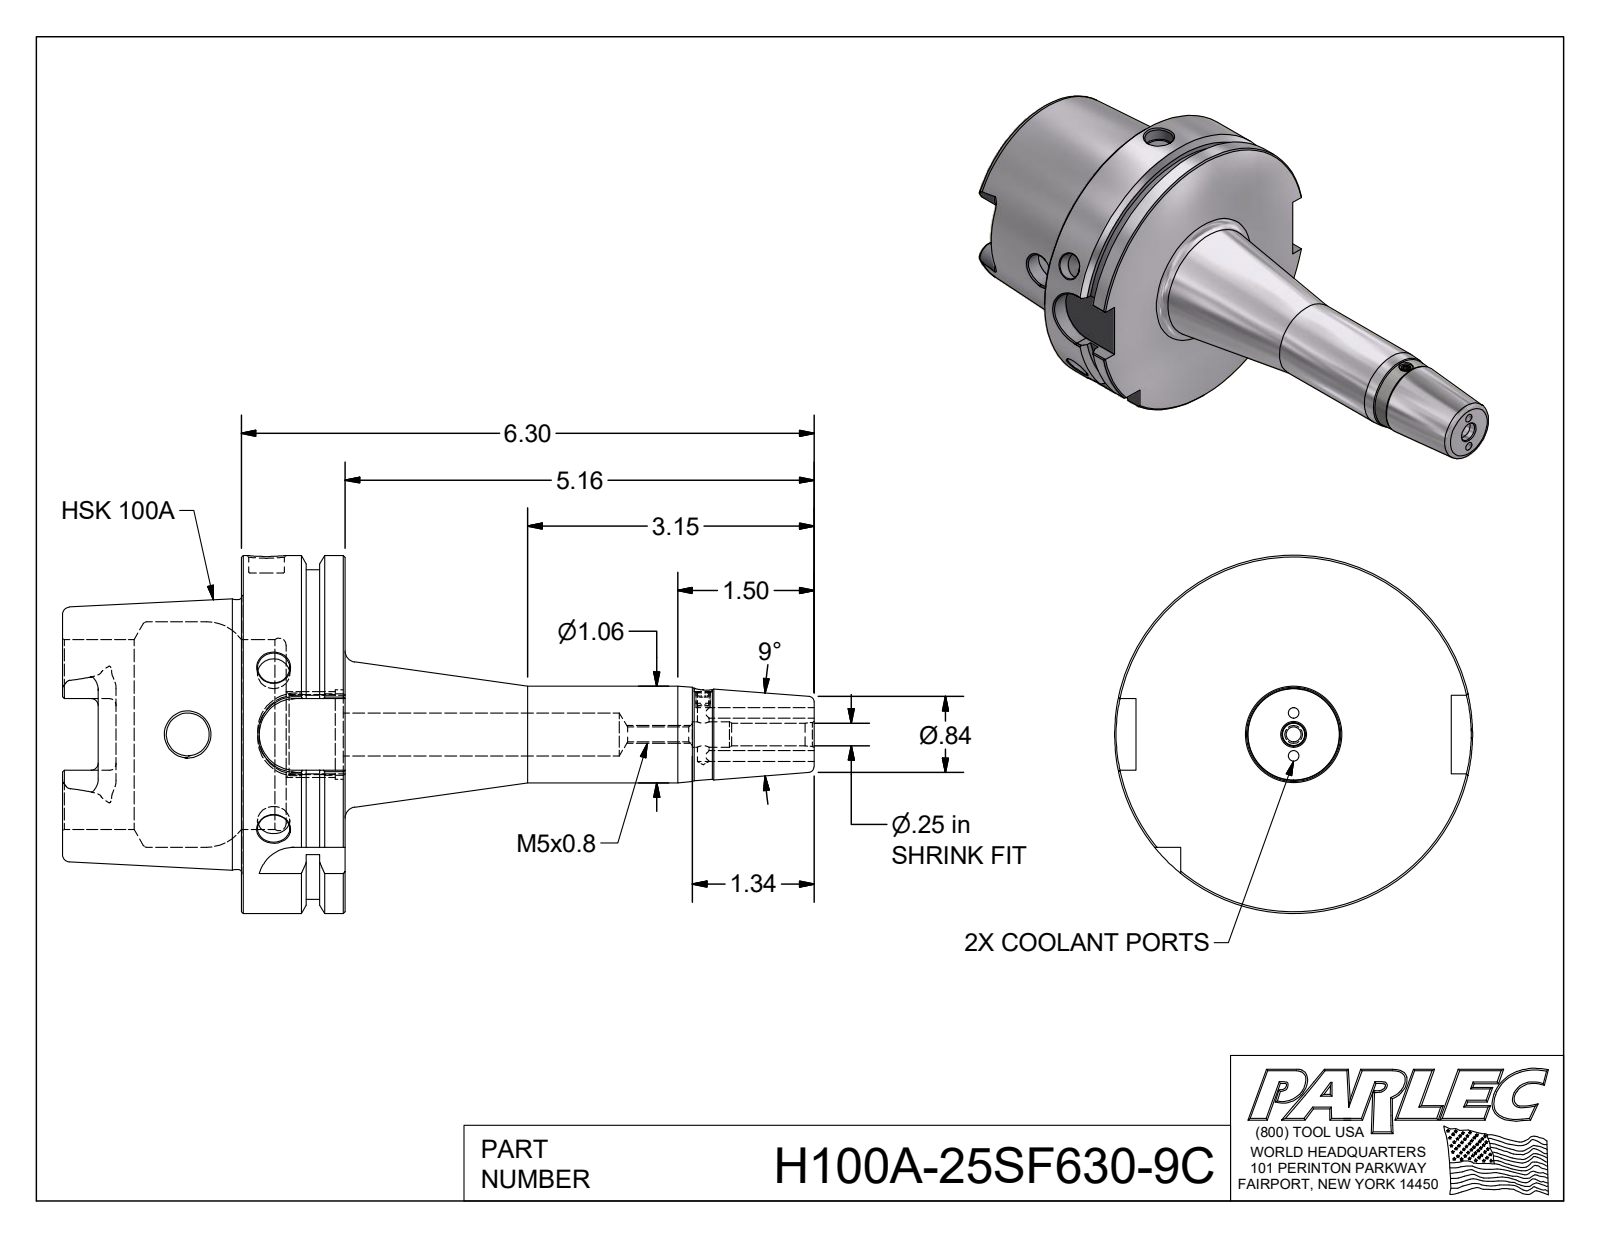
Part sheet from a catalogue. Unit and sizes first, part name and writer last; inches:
Units: inches
Overall size (bounding box): 8.268 × 3.937 × 3.937
Round holes (diameter × count): ⌀0.118 ×2, ⌀0.354 ×2, ⌀0.128 ×1, ⌀0.163 ×1, ⌀0.197 ×1, ⌀0.25 ×1, ⌀0.28 ×1, ⌀0.394 ×1, ⌀0.472 ×1, ⌀0.472 ×1, ⌀0.881 ×1, ⌀0.985 ×1
Round bosses / shafts (diameter × count): ⌀3.937 ×1, ⌀3.622 ×1, ⌀2.967 ×1, ⌀1.063 ×1
Partial cylindrical surfaces — rounded edges, fillets, slot ends (radius × count): R0.079 ×6, R0.192 ×4, R0.394 ×4
Main face-to-face distances: 1.142, 0.492, 0.65, 1.969, 2.461, 3.11, 3.465, 2.83, 0.861, 0.369
Hole centre spacings: 0.236, 0.472, 4.804
Volume: 20.26 in³ · Surface area: 101.3 in²
Bodies: 1 solid, 155 faces (49 planar, 42 cylindrical, 64 other)
STEP written by: Autodesk Inventor 2018 (AUTOMOTIVE_DESIGN)
